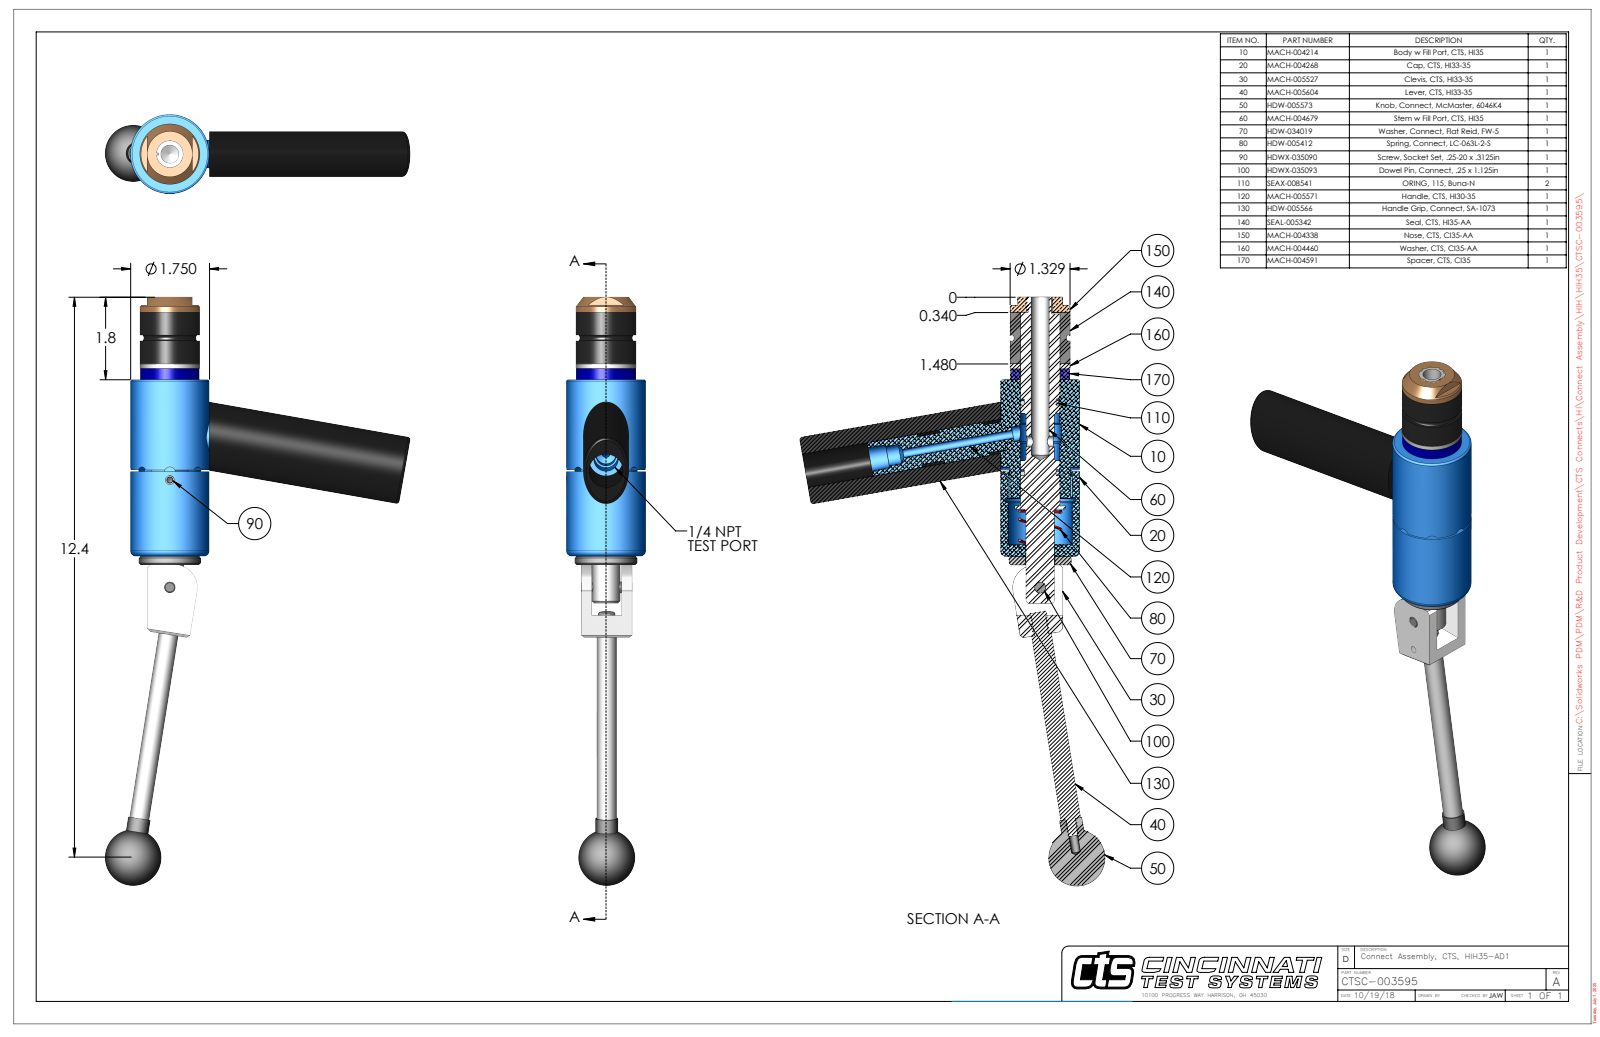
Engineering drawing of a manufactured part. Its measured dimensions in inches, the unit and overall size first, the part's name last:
Units: inches
Overall size (bounding box): 13.042 × 6.763 × 1.75
Round holes (diameter × count): ⌀0.201 ×2, ⌀0.15 ×1, ⌀0.187 ×1, ⌀0.249 ×1, ⌀0.25 ×1, ⌀0.251 ×1, ⌀0.313 ×1, ⌀0.406 ×1, ⌀0.438 ×1, ⌀0.531 ×1, ⌀0.635 ×1, ⌀0.656 ×1
Round bosses / shafts (diameter × count): ⌀0.25 ×2, ⌀1.75 ×1, ⌀1.38 ×1, ⌀1.329 ×1, ⌀1.312 ×1, ⌀0.869 ×1, ⌀0.75 ×1, ⌀0.625 ×1
Partial cylindrical surfaces — rounded edges, fillets, slot ends (radius × count): R0.125 ×4, R0.029 ×2, R0.166 ×1, R0.166 ×1, R0.249 ×1, R0.33 ×1, R0.5 ×1, R0.695 ×1
Main face-to-face distances: 3.915, 1.49, 5.405, 1.14, 0.35, 4.265, 1.25, 0.11, 0.24, 4.155
Hole centre spacings: 0.74, 2.376, 3.116
Volume: 18.81 in³ · Surface area: 125.7 in²
Bodies: 11 solids, 308 faces (110 planar, 128 cylindrical, 70 other)
Part name (STEP PRODUCT): CTSC-003595
STEP written by: SolidWorks 2023 (AUTOMOTIVE_DESIGN)
